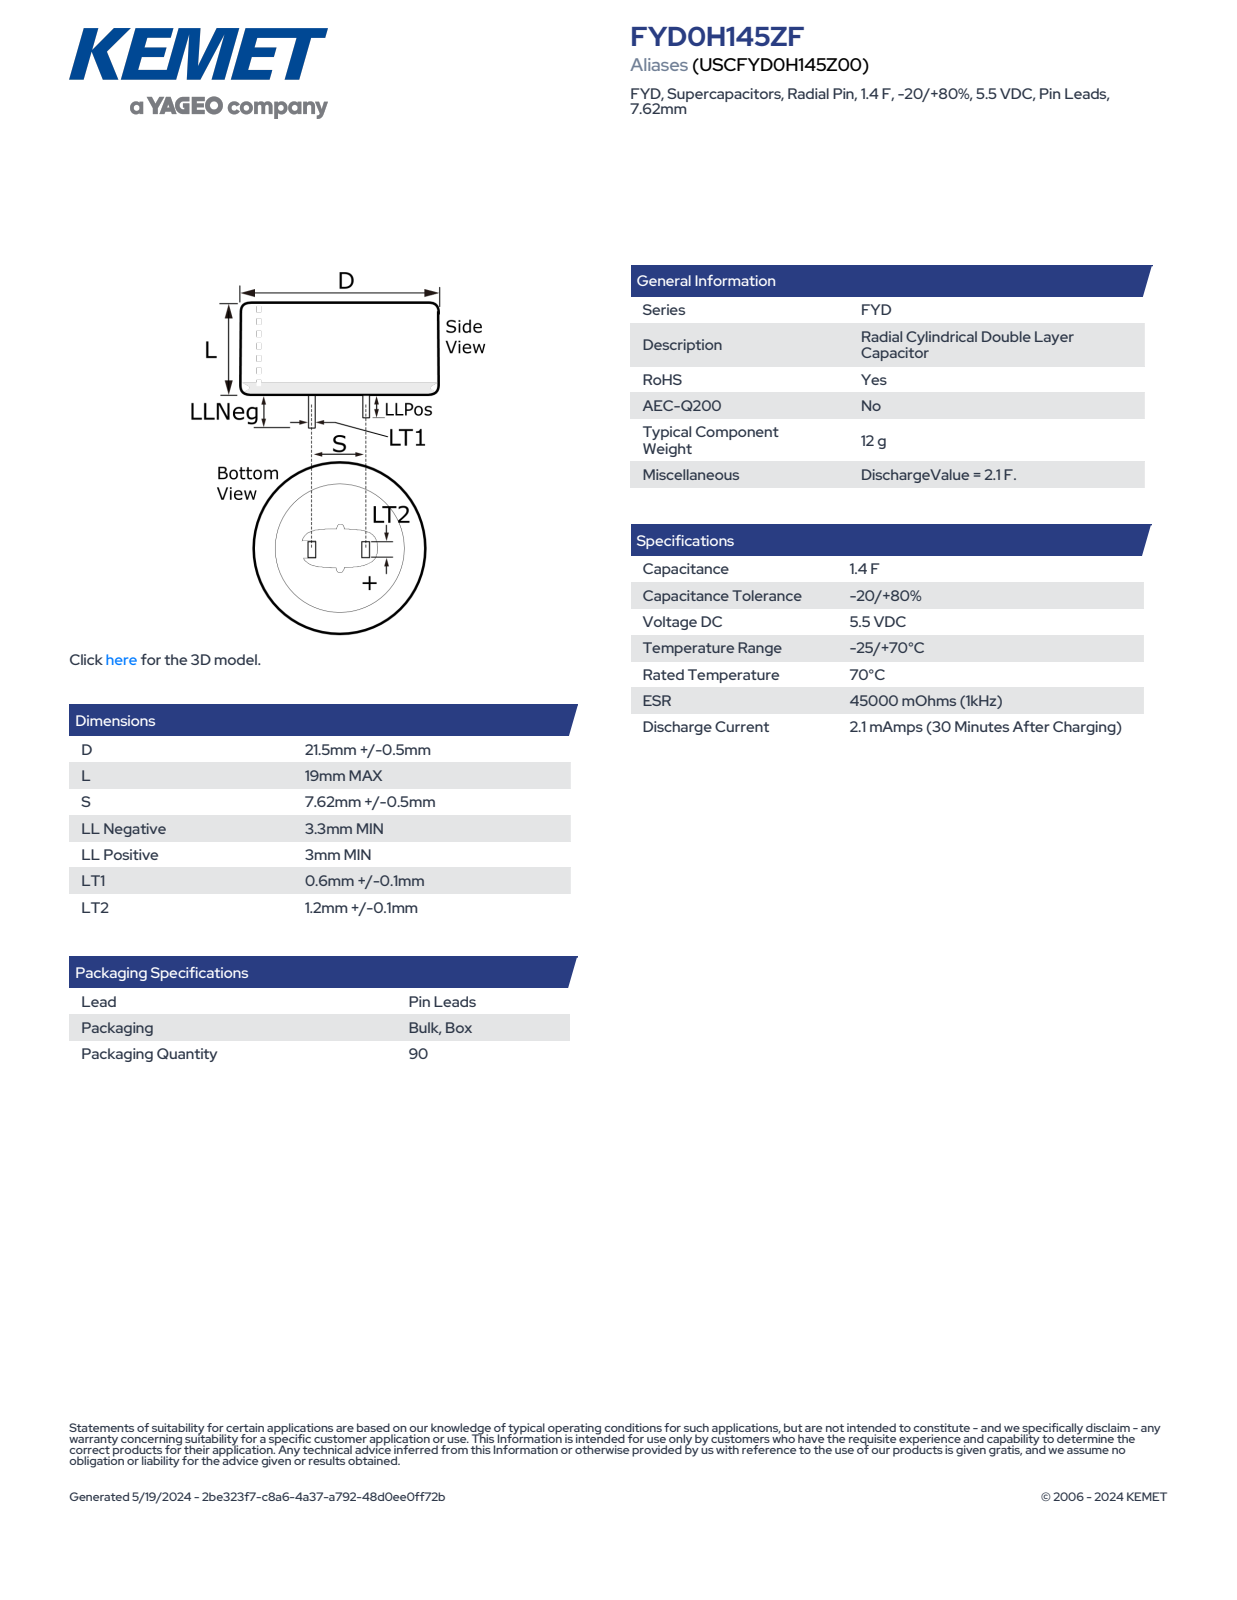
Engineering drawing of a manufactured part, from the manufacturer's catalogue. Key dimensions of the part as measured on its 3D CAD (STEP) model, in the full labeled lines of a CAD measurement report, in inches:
Part name (STEP PRODUCT): CDR_LPLLN_D22L19S7.62LLNEG3.3LLPOS3LT10.7LT21.3
STEP written by: SolidWorks 2014 (AUTOMOTIVE_DESIGN)
Units: inches
Bodies: 1 solid, 78 faces (70 planar, 4 cylindrical, 4 other)
Overall size (bounding box): 0.878 × 0.866 × 0.866
Volume: 0.438 in³ · Surface area: 3.139 in²
Round bosses / shafts (diameter × count): ⌀0.866 ×1
Partial cylindrical surfaces — rounded edges, fillets, slot ends (radius × count): R0.433 ×1
Main face-to-face distances: 0.748, 0.748, 0.028, 0.3, 0.051, 0.328, 0.272, 0.13, 0.878, 0.878
